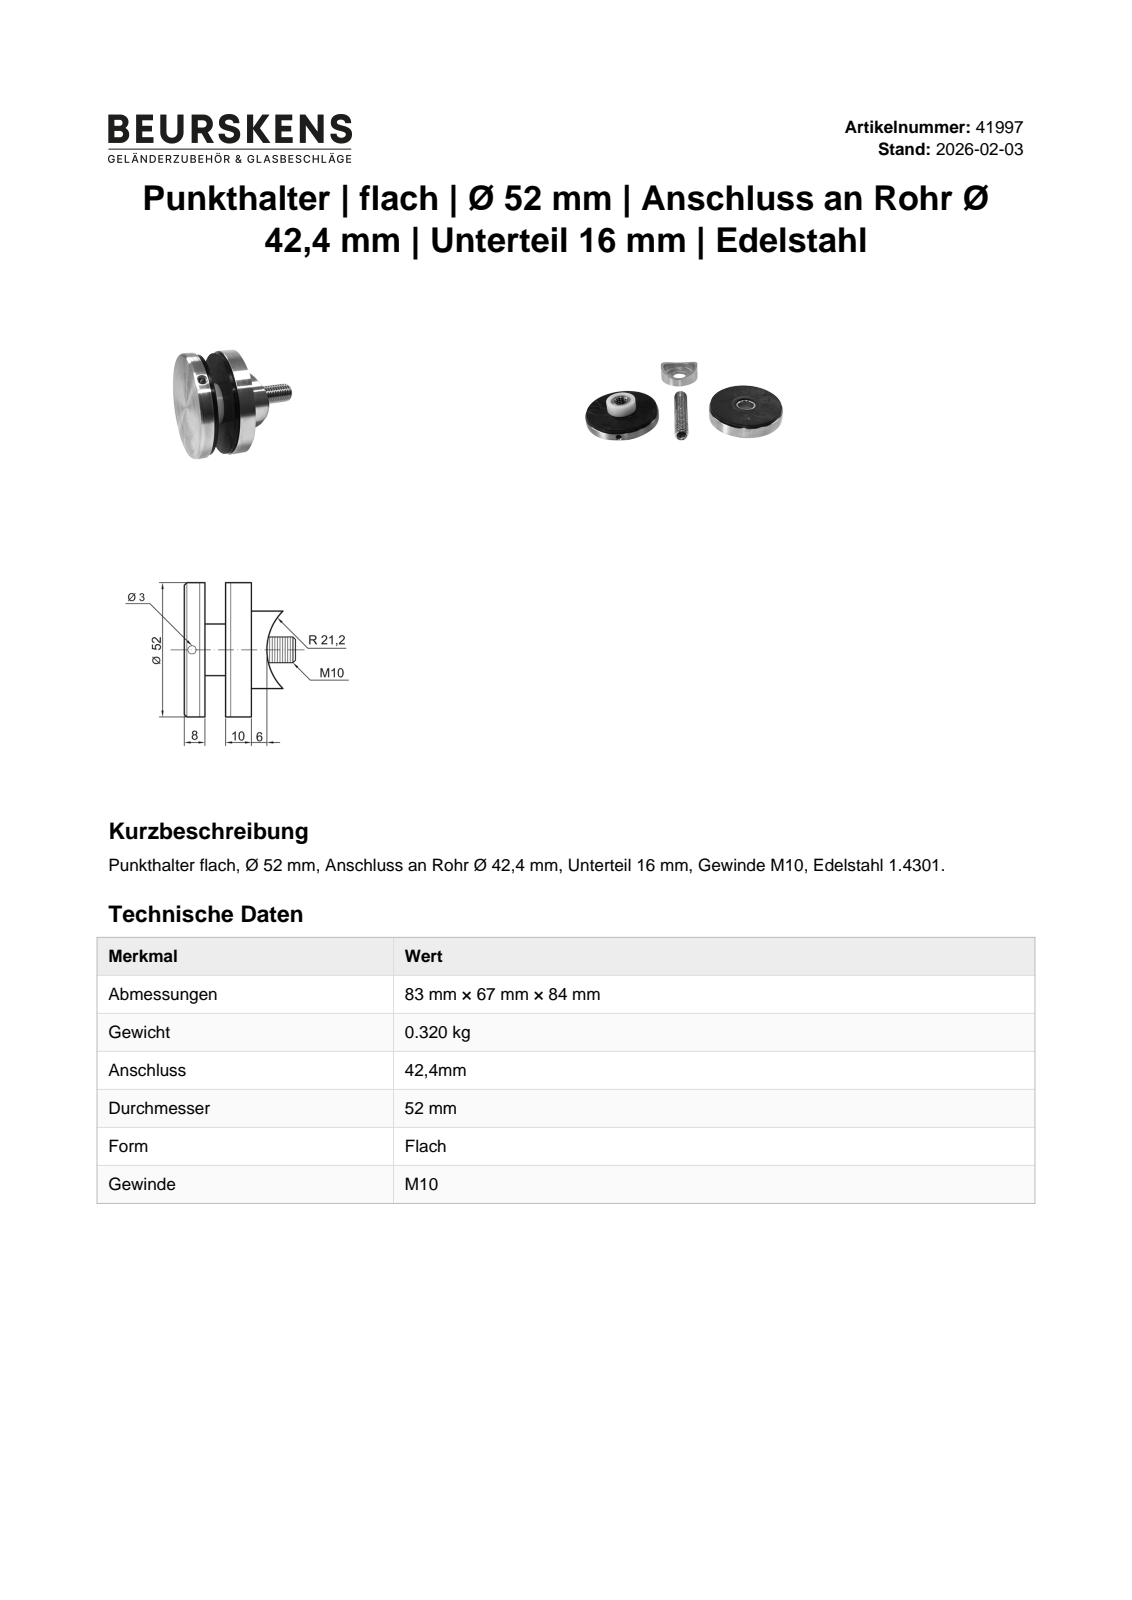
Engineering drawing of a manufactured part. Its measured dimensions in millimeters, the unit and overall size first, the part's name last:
Units: millimetres
Overall size (bounding box): 52 × 52 × 38.22
Round holes (diameter × count): ⌀3 ×1, ⌀10 ×1, ⌀10.5 ×1, ⌀14 ×1, ⌀14.2 ×1, ⌀24 ×1
Round bosses / shafts (diameter × count): ⌀52 ×1, ⌀50 ×1, ⌀30 ×1, ⌀20.2 ×1
Partial cylindrical surfaces — rounded edges, fillets, slot ends (radius × count): R21.2 ×1
Main face-to-face distances: 8, 10, 2, 18, 12, 20, 6, 16, 26, 3
Volume: 41 520 mm³ · Surface area: 23 601 mm²
Bodies: 6 solids, 38 faces (17 planar, 18 cylindrical, 3 other)
Part name (STEP PRODUCT): 41997; Kopf 41730; 40902; 40910 Kunststoff weiß (+2 more)
STEP written by: Autodesk Inventor 2023 (AUTOMOTIVE_DESIGN)
